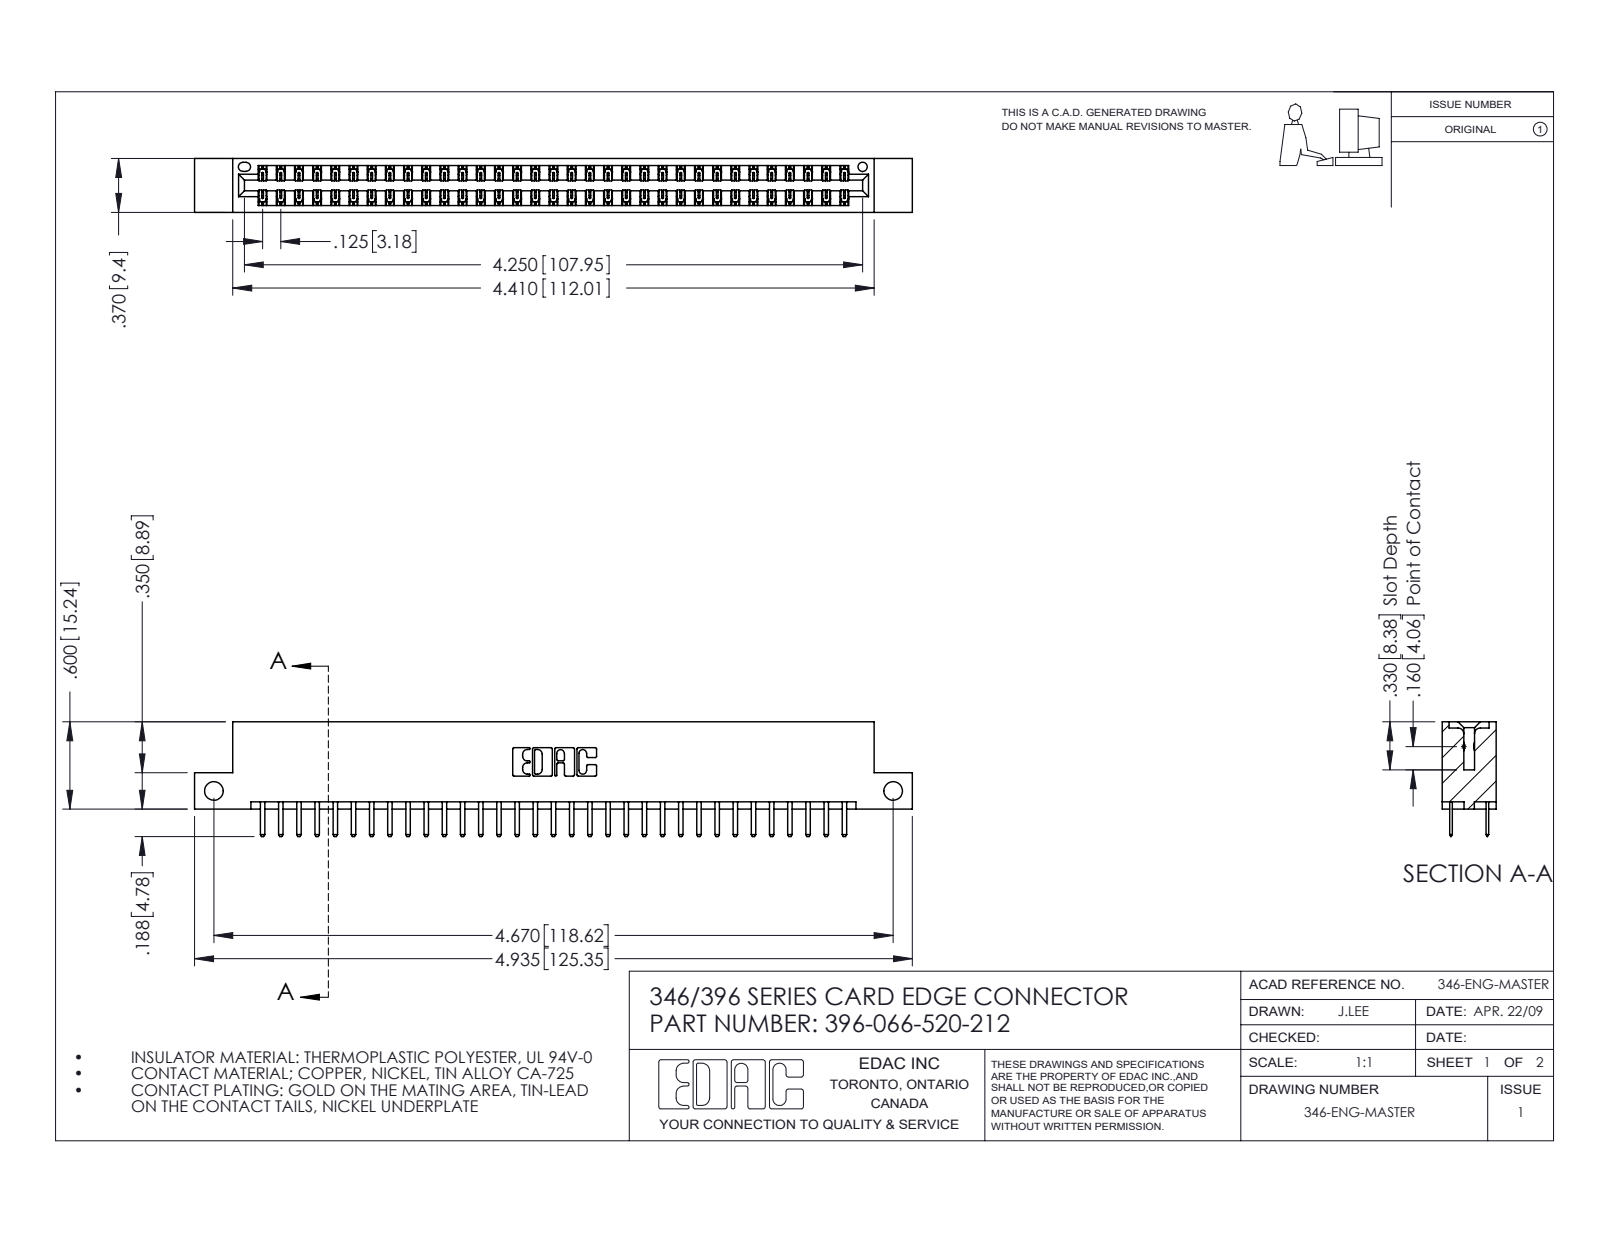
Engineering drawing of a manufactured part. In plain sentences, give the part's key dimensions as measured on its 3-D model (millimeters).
The part is named "345-292-001_345-293-120; 396-066-520-212; 346 Part_Flush Mounting Lugs - Side Mount". Its 3-D file was written by "SolidWorks 2016 (CONFIG_CONTROL_DESIGN)". It is 67 solids with 3818 faces: 2518 planar, 1300 cylindrical and 0 other. Overall it measures 125.3 by 20 by 9.4 millimeters. Its volume is 12 000 cubic millimeters and its surface area 16 200 square millimeters. Round holes: 2 of diameter 3.3, 1 of diameter 1.6. Partial cylindrical surfaces (rounded edges, fillets, slot ends): 99 of radius 0.2, 70 of radius 0.3, 22 of radius 0.3, 6 of radius 0.2, 6 of radius 0.8, 3 of radius 0.7, 2 of radius 0.4, 2 of radius 0.6. The main face-to-face distances are 1.2, 8.2, 6.4, 9.4, 7, 1.8, 7.6, 0.6, 3.8, 5.6. The hole center spacings are 118.6.
